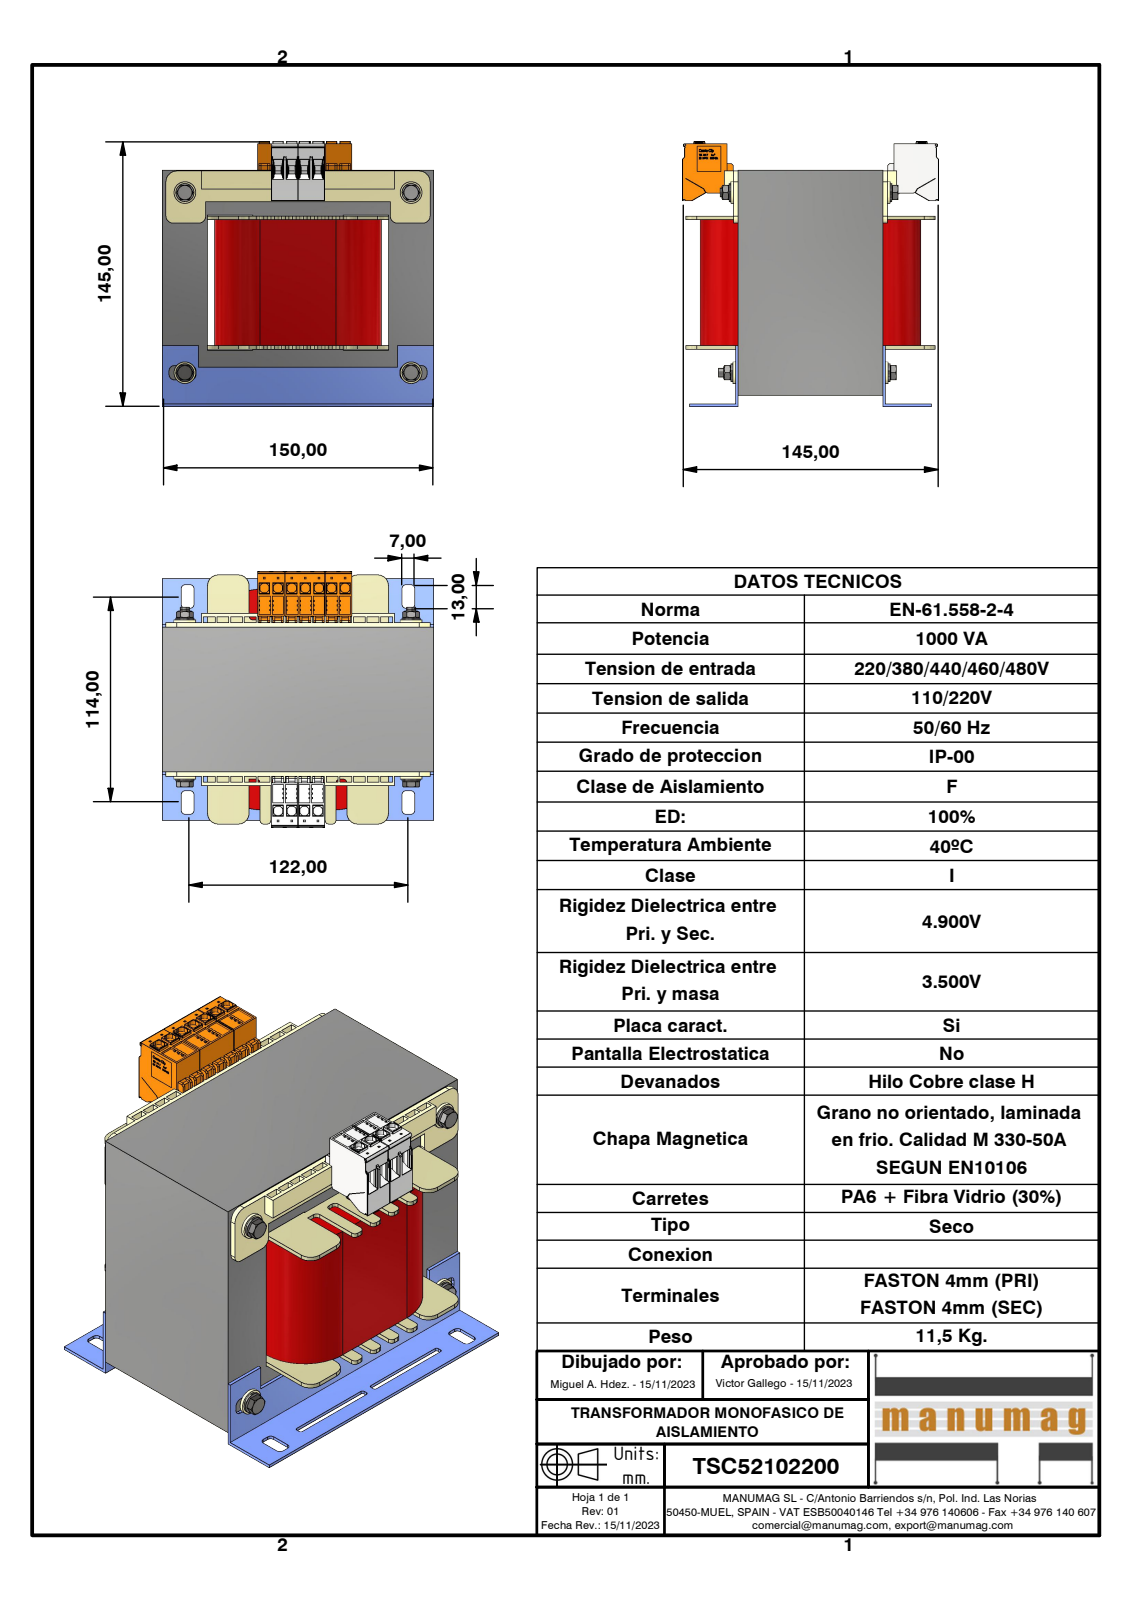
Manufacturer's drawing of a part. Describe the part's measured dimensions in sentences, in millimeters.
The part is named "TSC52102200; EI150 x 125 - 80 (RC50); EI 150 X 125 - 80; AF50DIN (+8 more)". Its 3-D file was written by "Autodesk Inventor 2023 (AUTOMOTIVE_DESIGN)". It is 35 solids with 9258 faces: 7534 planar, 1165 cylindrical and 559 other. Overall it measures 150 by 147.4 by 141.9 millimeters. Its volume is 1 781 000 cubic millimeters and its surface area 283 756 square millimeters. Round holes: 4 of diameter 4.13, 4 of diameter 5, 4 of diameter 5.3, 4 of diameter 8. Round bosses or shafts: 4 of diameter 12, 4 of diameter 10, 4 of diameter 6.7, 4 of diameter 5.9, 4 of diameter 4.57. Partial cylindrical surfaces (rounded edges, fillets, slot ends): 431 of radius 0.15, 122 of radius 0.2, 51 of radius 2, 30 of radius 0.5, 24 of radius 1, 12 of radius 0.3, 11 of radius 2.7, 10 of radius 5. The main face-to-face distances are 25, 100, 50, 80, 125, 99.5, 75, 25.5, 1.5, 2.5. The hole center spacings are 100, 125, 160.08.
